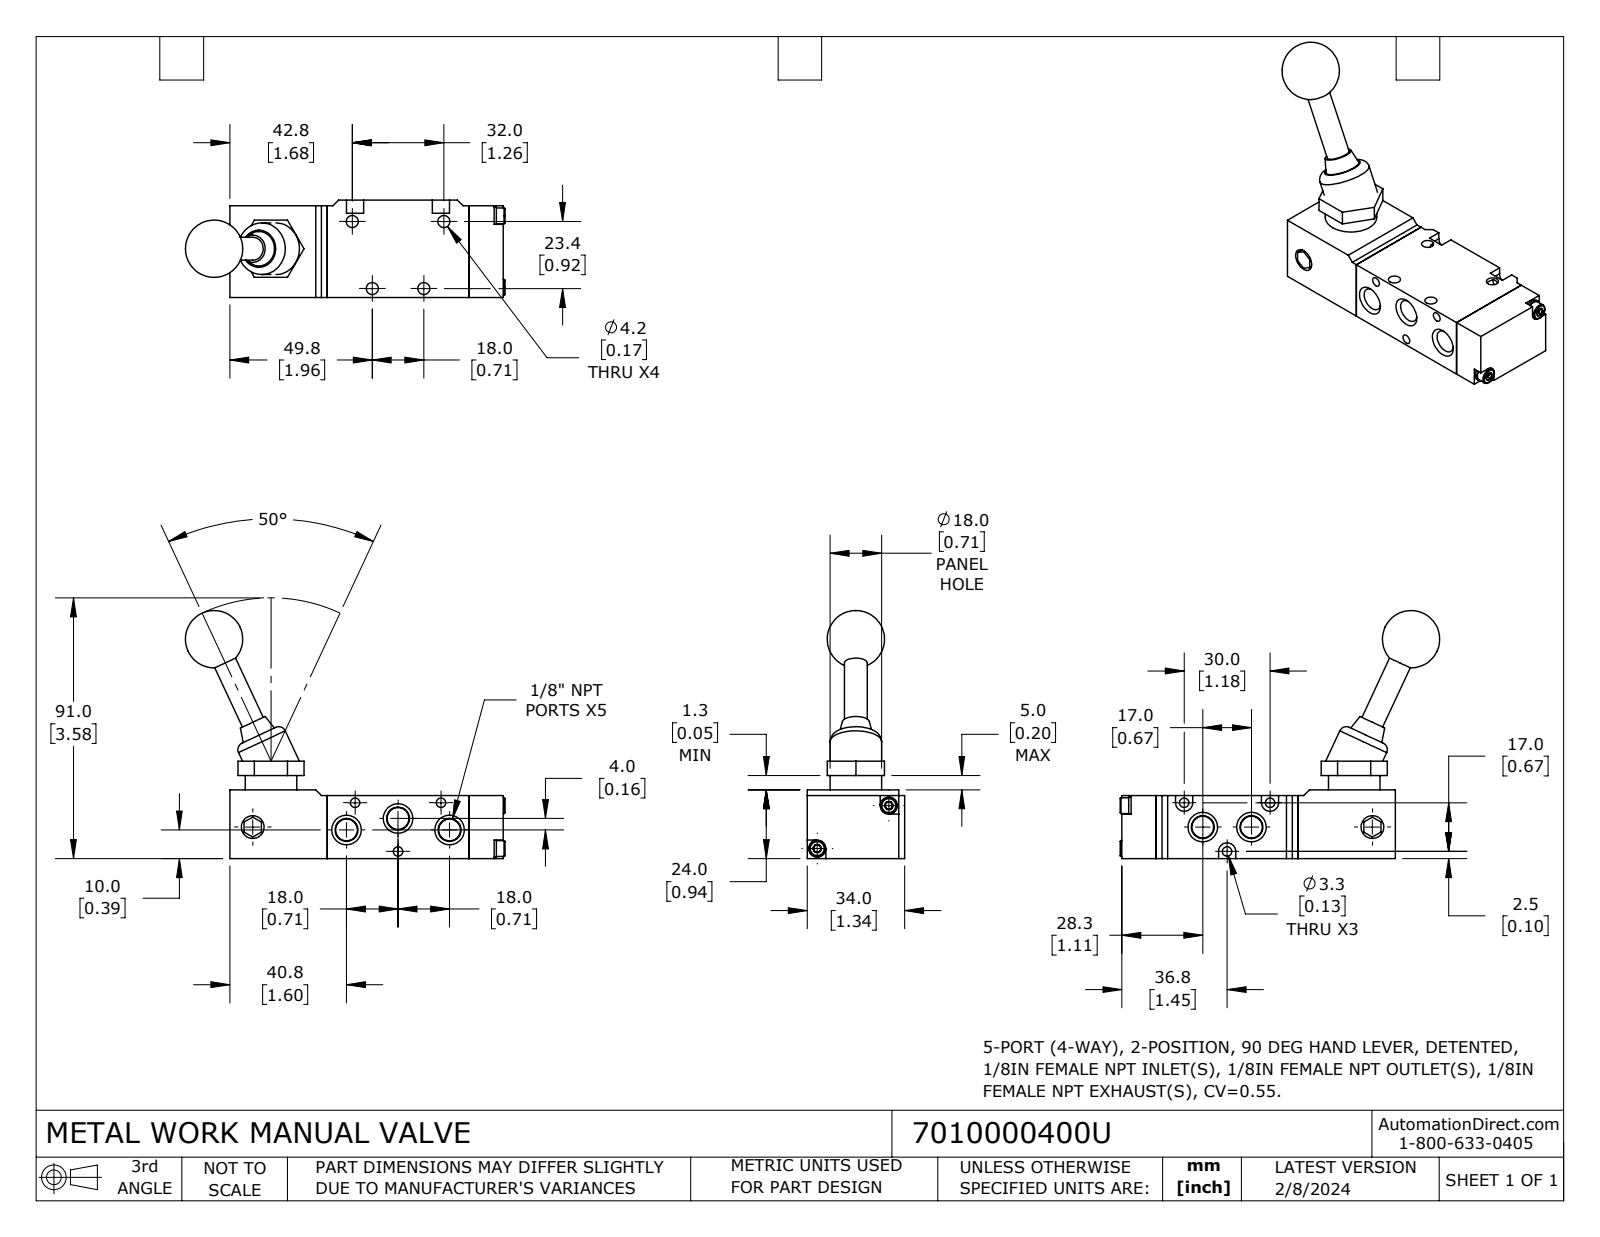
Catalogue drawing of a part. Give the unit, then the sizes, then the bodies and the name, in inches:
Units: inches
Overall size (bounding box): 4.393 × 3.409 × 1.339
Round holes (diameter × count): ⌀0.165 ×4, ⌀0.13 ×3, ⌀0.118 ×2, ⌀0.313 ×1
Round bosses / shafts (diameter × count): ⌀0.709 ×2, ⌀0.236 ×2, ⌀0.217 ×2, ⌀0.315 ×1
Partial cylindrical surfaces — rounded edges, fillets, slot ends (radius × count): R0.118 ×3
Main face-to-face distances: 0.866, 1.339, 1.949, 0.079, 1.26, 0.472, 3.287, 0.945, 2.421, 3.76
Hole centre spacings: 0.893, 0.961, 1.348, 0.709, 1.148, 1.181, 1.26, 1.447
Volume: 4.828 in³ · Surface area: 34.88 in²
Bodies: 8 solids, 208 faces (105 planar, 49 cylindrical, 54 other)
Part name (STEP PRODUCT): 7010000400U
STEP written by: SolidWorks 2023 (CONFIG_CONTROL_DESIGN)
